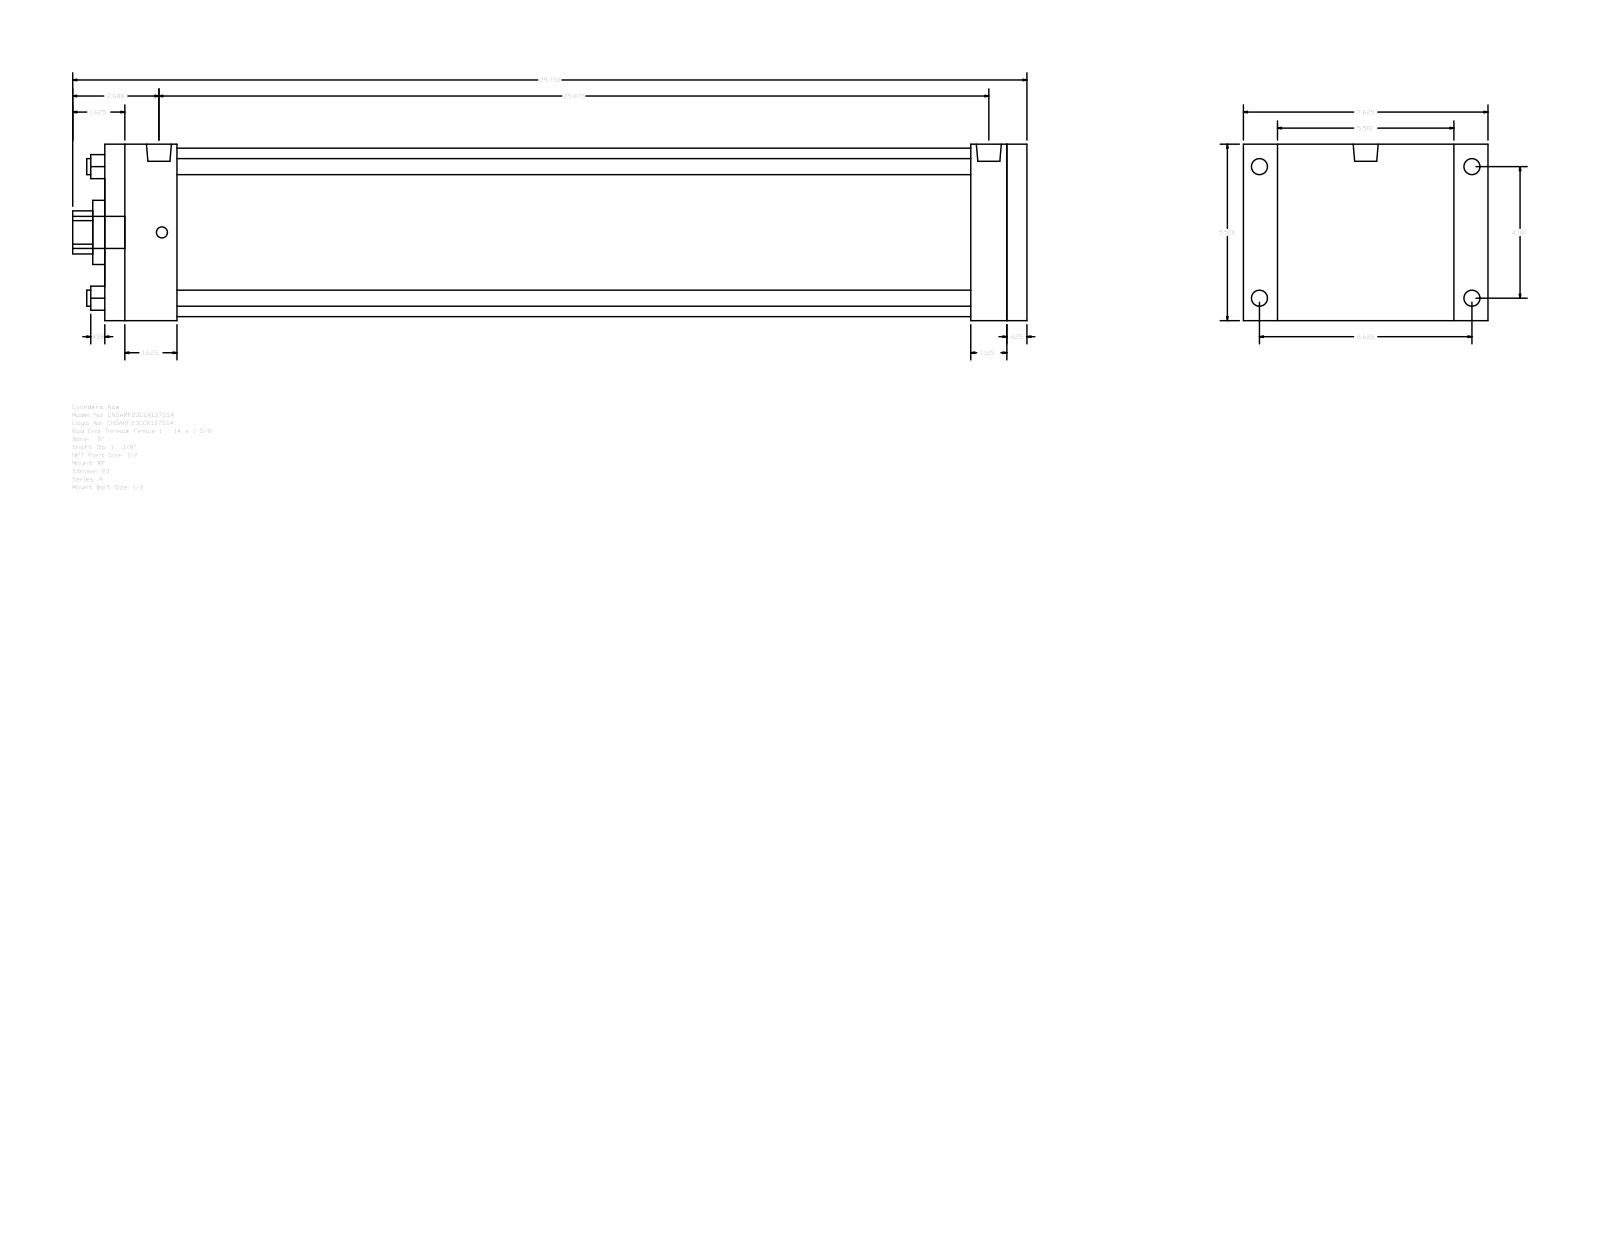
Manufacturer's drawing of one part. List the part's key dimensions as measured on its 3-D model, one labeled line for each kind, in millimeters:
Part name (STEP PRODUCT): A_RF__0500_1.375
STEP written by: GSSL Pune (CONFIG_CONTROL_DESIGN)
Units: millimetres
Bodies: 0 solids, 92 faces (64 planar, 28 cylindrical, 0 other)
Overall size (bounding box): 755.65 × 193.68 × 139.7
Round holes (diameter × count): ⌀12.7 ×4, ⌀34.92 ×1, ⌀50.8 ×1, ⌀133.35 ×1
Round bosses / shafts (diameter × count): ⌀12.7 ×4, ⌀8.73 ×4, ⌀19.77 ×2, ⌀25.4 ×1
Partial cylindrical surfaces — rounded edges, fillets, slot ends (radius × count): R17.06 ×1
Main face-to-face distances: 139.7, 730.25, 15.88, 714.37, 28.57, 57.15, 657.22, 673.1, 685.8, 628.65
Hole centre spacings: 73.64, 104.14, 147.28
